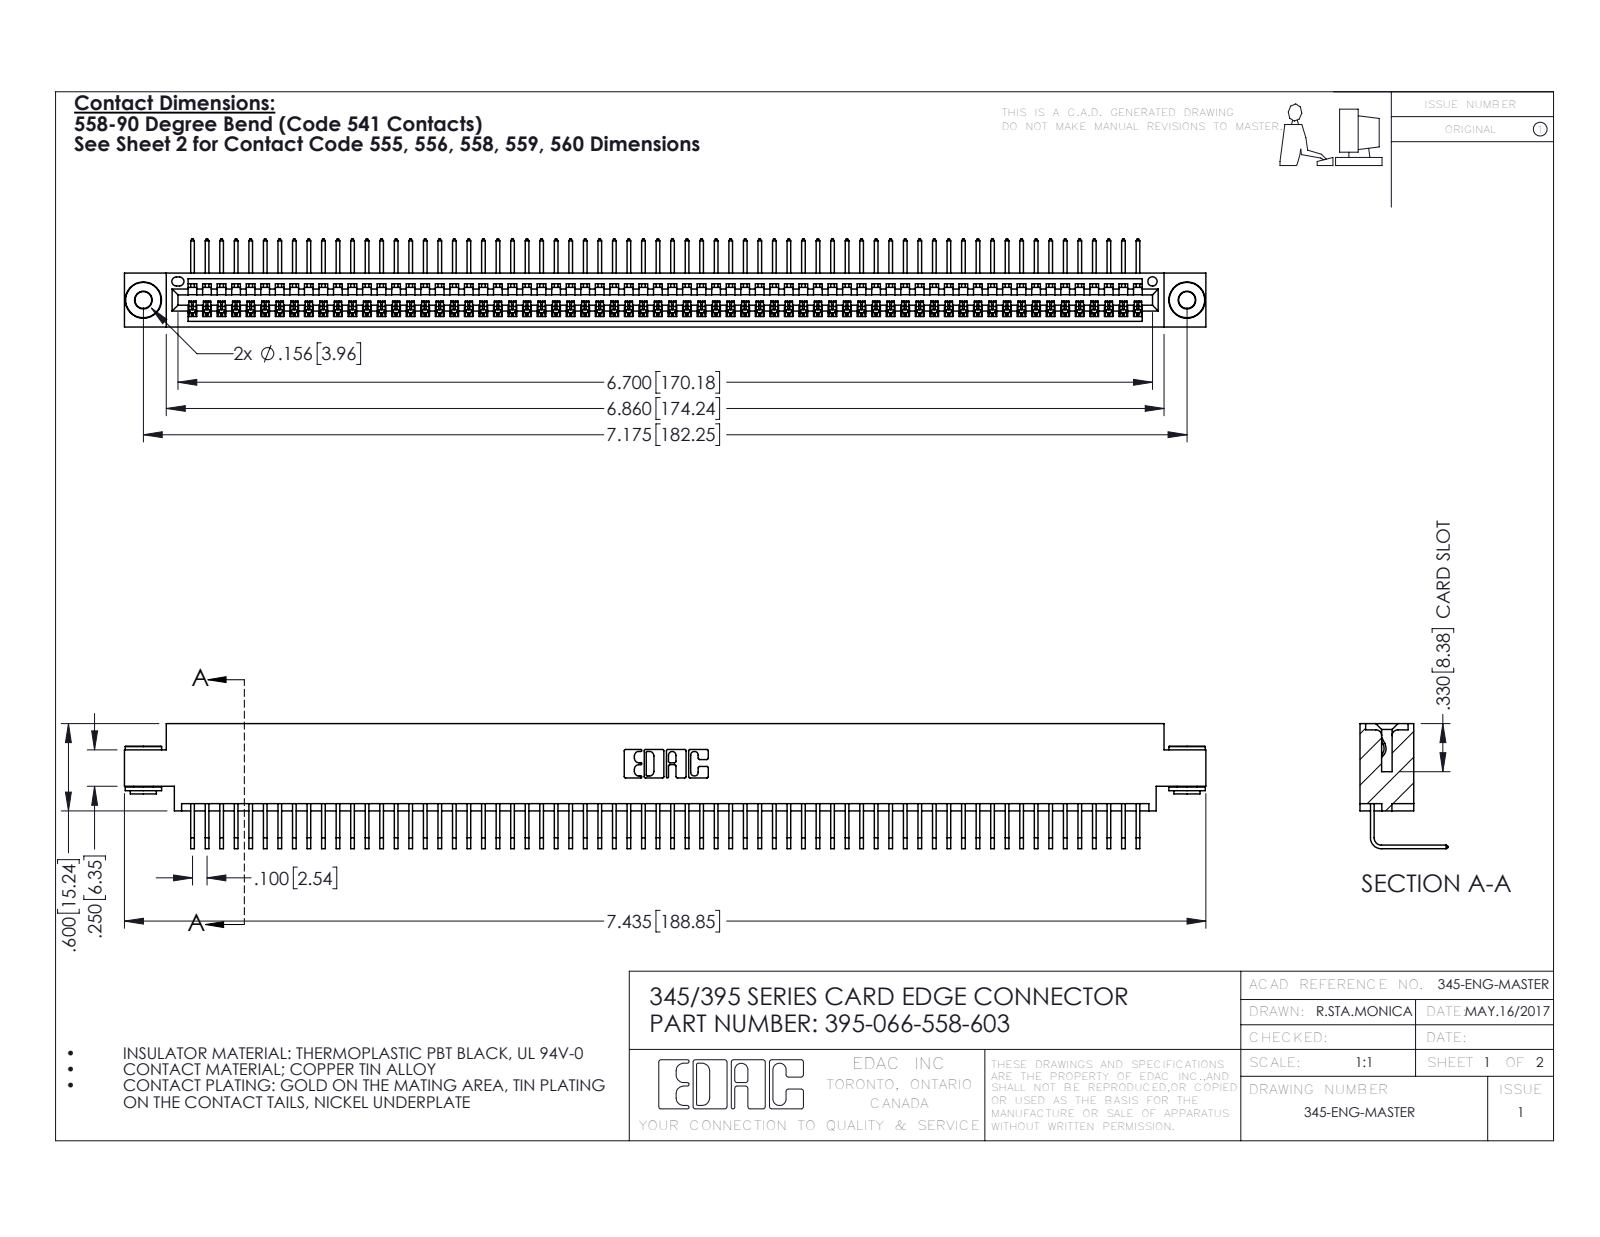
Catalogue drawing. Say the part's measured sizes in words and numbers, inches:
The part is named "395-066-558-603; 345 Part_0.170 Offset - 0.156 Dia-TH; 345-250-002_345-250-002-102; 345-292-001_558 Tail - 2". Its 3-D file was written by "SolidWorks 2016 (CONFIG_CONTROL_DESIGN)". It is 69 solids with 4128 faces: 2866 planar, 1254 cylindrical and 8 other. Overall it measures 7.435 by 0.859 by 0.605 inches. Its volume is 1.114 cubic inches and its surface area 40.65 square inches. Round holes: 2 of diameter 0.116, 2 of diameter 0.156, 1 of diameter 0.064. Round bosses or shafts: 2 of diameter 0.25, 2 of diameter 0.18, 2 of diameter 0.136. Partial cylindrical surfaces (rounded edges, fillets, slot ends): 132 of radius 0.006, 22 of radius 0.01, 6 of radius 0.007, 6 of radius 0.031, 3 of radius 0.026, 2 of radius 0.031, 2 of radius 0.04, 1 of radius 0.014. The main face-to-face distances are 0.072, 0.298, 0.37, 0.2, 0.098, 0.272, 0.025, 0.225, 0.175, 0.149. The hole center spacings are 0.27, 6.939, 7.175.
